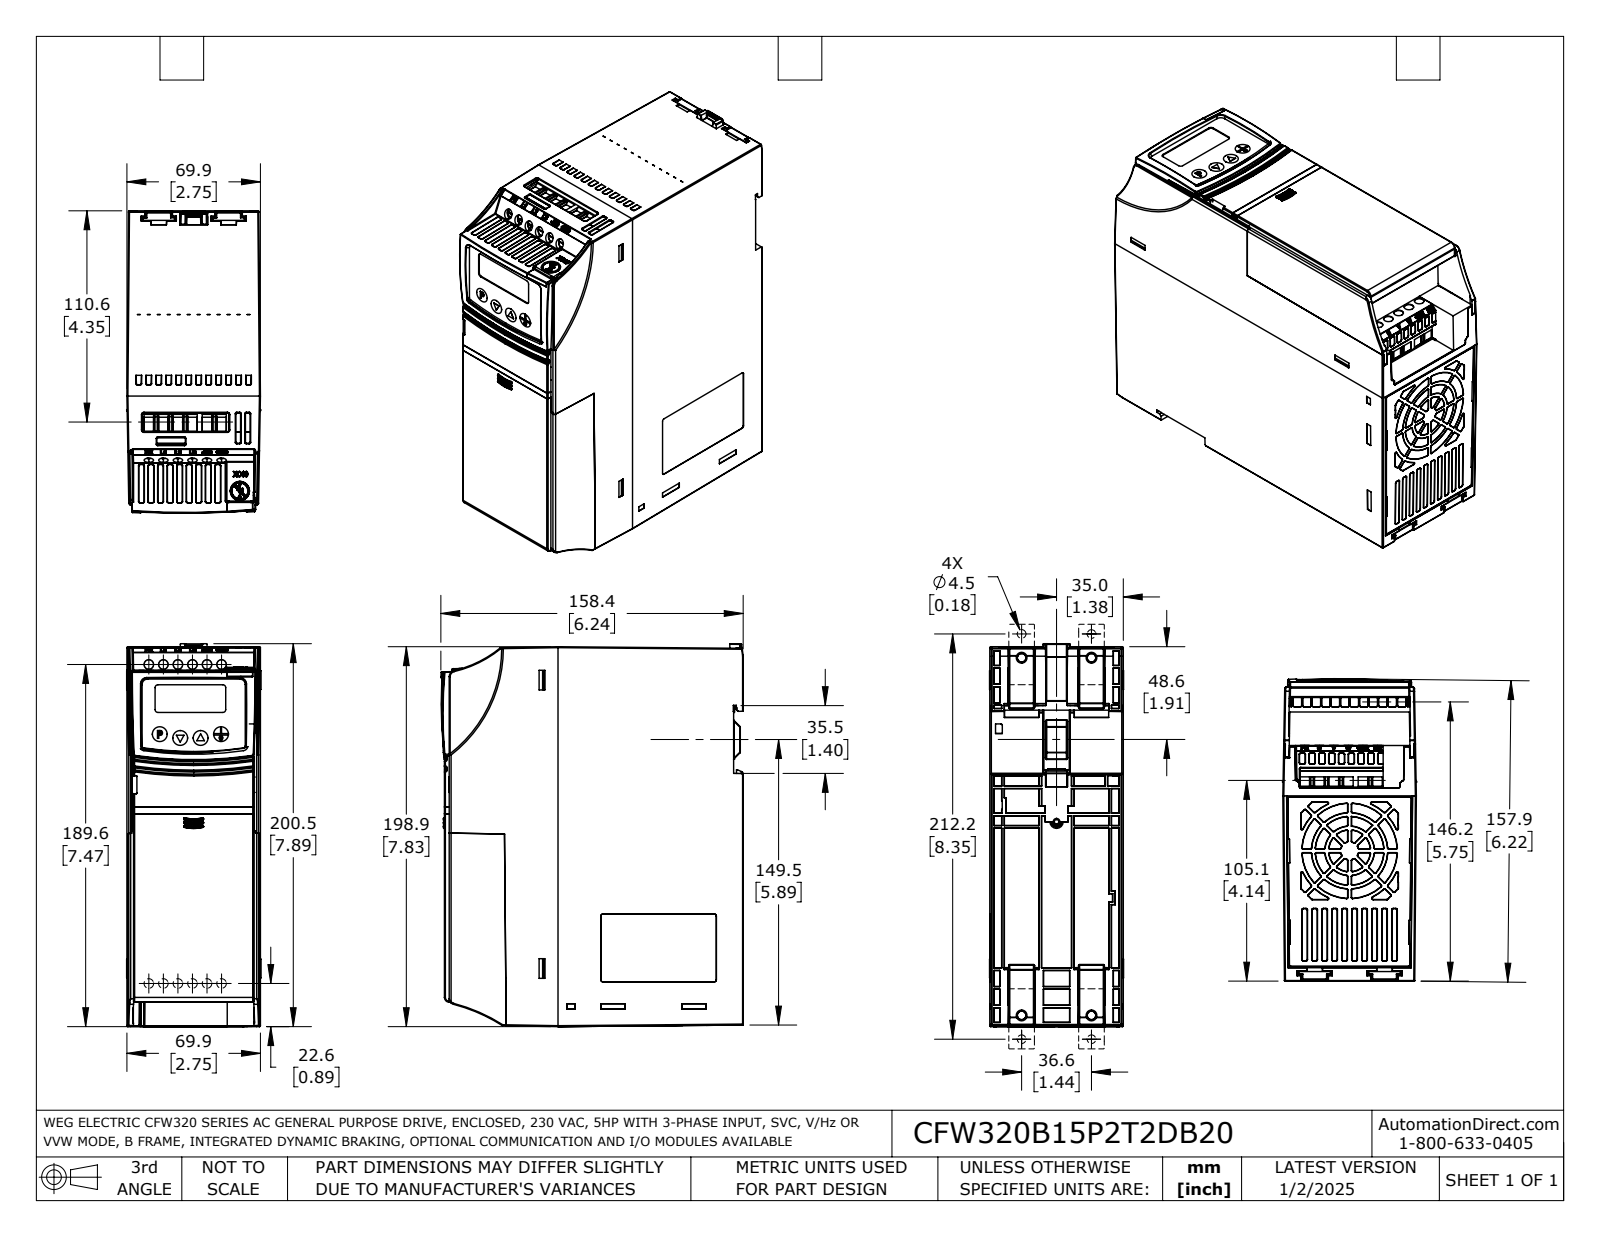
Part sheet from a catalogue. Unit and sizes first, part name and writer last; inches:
Units: inches
Overall size (bounding box): 7.894 × 6.235 × 2.764
Round holes (diameter × count): ⌀0.193 ×6
Partial cylindrical surfaces — rounded edges, fillets, slot ends (radius × count): R0.012 ×355, R0.02 ×181, R0.039 ×14, R0.03 ×7, R0.118 ×5, R0.01 ×2, R0.109 ×2, R0.098 ×1
Main face-to-face distances: 0.209, 0.098, 0.1, 5.826, 5.728, 0.211, 5.939, 6.037, 7.5, 0.039
Hole centre spacings: 0.3, 0.6, 0.9, 1.2, 1.5
Volume: 24.51 in³ · Surface area: 385.1 in²
Bodies: 5 solids, 3984 faces (1907 planar, 899 cylindrical, 1178 other)
Part name (STEP PRODUCT): CFW320B15P2T2DB20
STEP written by: SolidWorks 2021 (AUTOMOTIVE_DESIGN)
